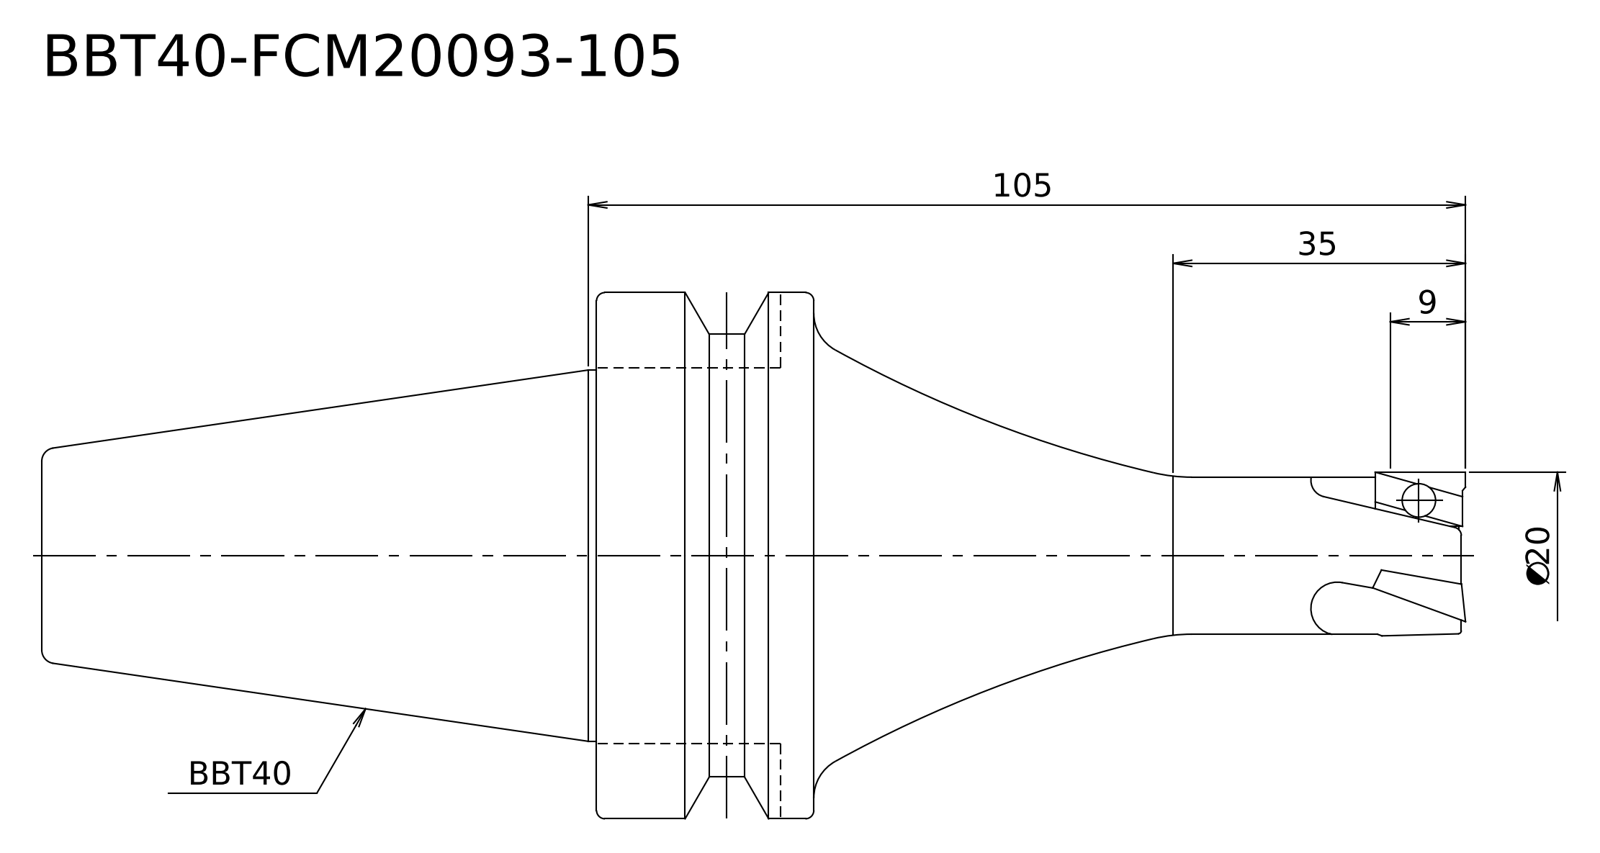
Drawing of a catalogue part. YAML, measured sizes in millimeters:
step_written_by: "Kubotek KeyCreator V8.5.1 (14335) (CONFIG_CONTROL_DESIGN)"
units: millimeters
bodies: {solids: 1, faces: 17, planar: 4, cylindrical: 6, other: 7}
overall_size: [170.4, 63, 63]
volume: 194710
surface_area: 23769
round_bosses_or_shafts:
  - {diameter: 63, count: 1}
  - {diameter: 53, count: 1}
  - {diameter: 44.45, count: 1}
  - {diameter: 20, count: 1}
  - {diameter: 18.8, count: 1}
face_to_face_distances: [66.4, 26, 92.4, 78, 104, 170.4]
